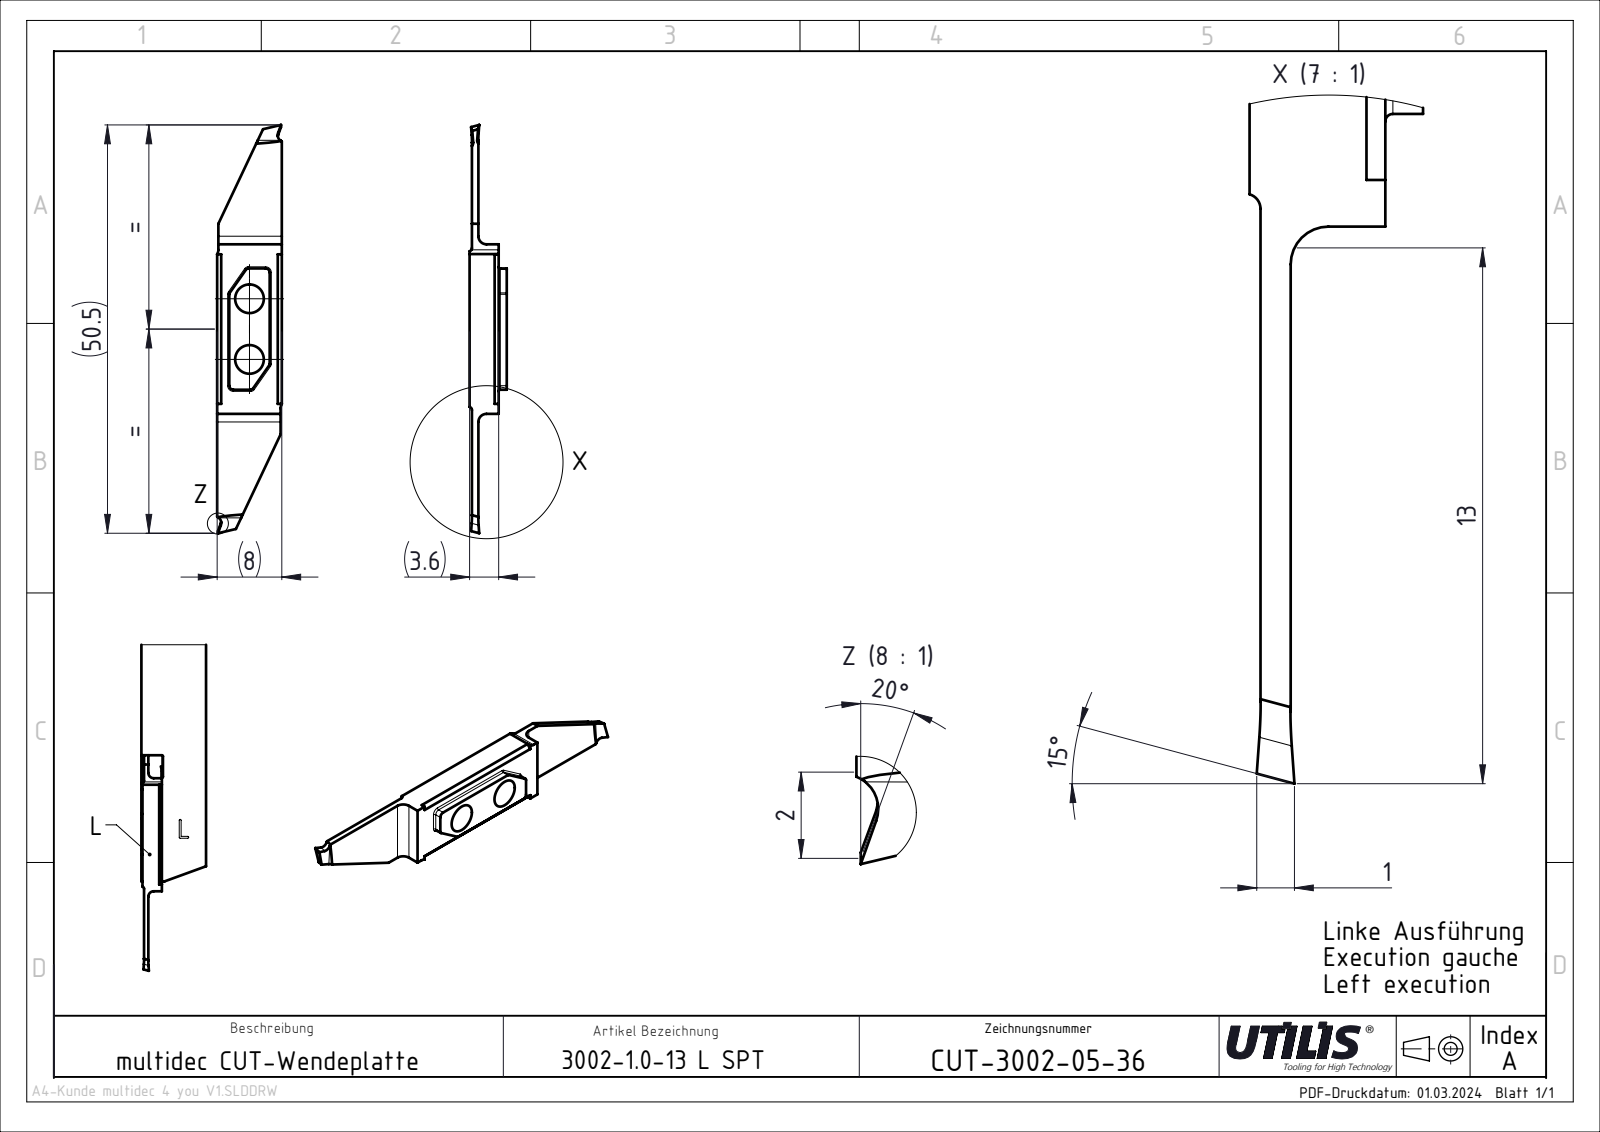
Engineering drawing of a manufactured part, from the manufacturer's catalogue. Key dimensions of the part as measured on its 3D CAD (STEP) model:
Part name (STEP PRODUCT): CUT-3002 SPT Slim_and_Deep; ASME Y14.5
STEP written by: SolidWorks 2023 SP4 || FormatWorks Professional (AP242_MANAGED_MODEL_BASED_3D_ENGINEERING_MIM_LF)
Units: millimetres
Bodies: 1 solid, 36 faces (26 planar, 10 cylindrical, 0 other)
Overall size (bounding box): 50.5 × 8 × 3.6
Volume: 656 mm³ · Surface area: 926 mm²
Round holes (diameter × count): ⌀3.55 ×2
Partial cylindrical surfaces — rounded edges, fillets, slot ends (radius × count): R1 ×4, R0.4 ×2
Main face-to-face distances: 0.8, 1.09, 3.6, 3.31, 2.51, 8, 20.98, 18.09, 7.85, 1.62
Hole centre spacings: 7.5
